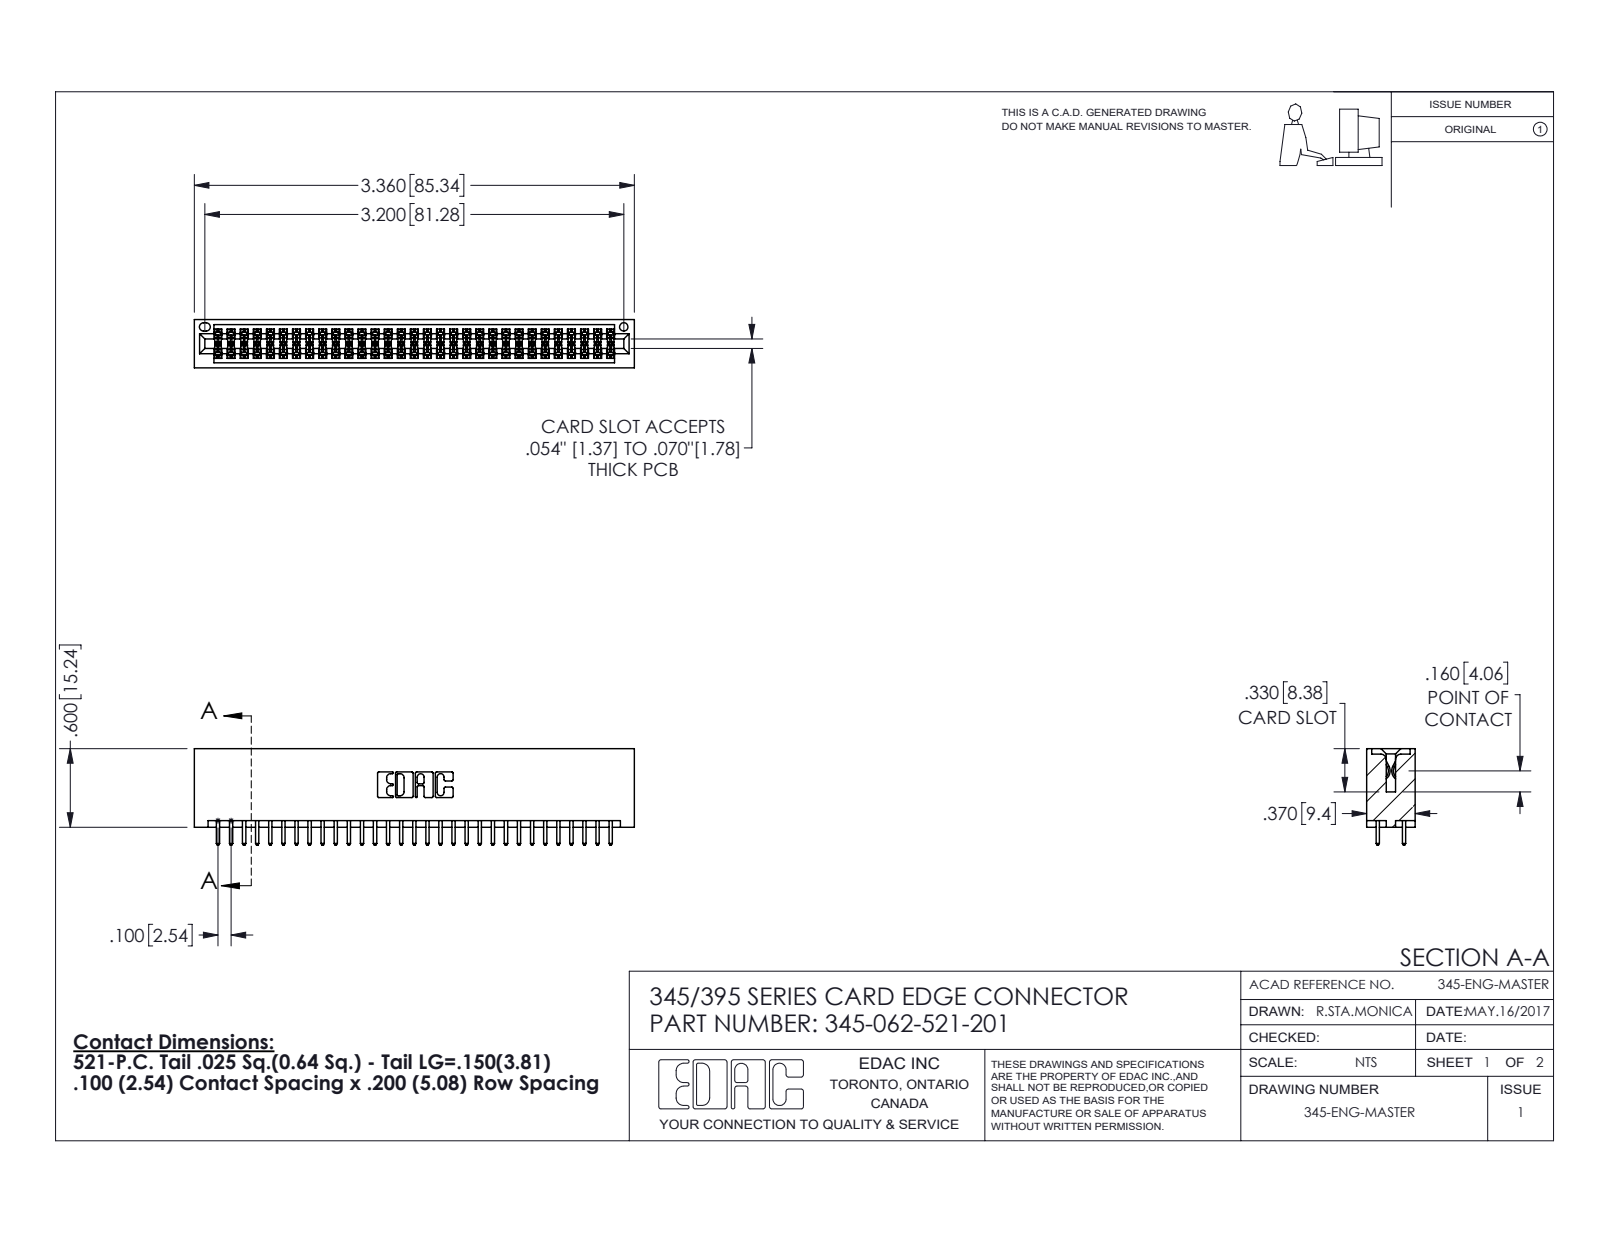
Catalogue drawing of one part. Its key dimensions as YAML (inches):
part_name: "345 Part_No Mounting Lugs; 345-292-001_345-293-121; 345-062-521-201"
step_written_by: "SolidWorks 2016 (CONFIG_CONTROL_DESIGN)"
units: inches
bodies: {solids: 63, faces: 3218, planar: 2122, cylindrical: 1096, other: 0}
overall_size: [3.36, 0.737, 0.37]
volume: 0.536
surface_area: 20
round_holes:
  - {diameter: 0.064, count: 1}
partial_cylinders:
  - {radius: 0.006, count: 93}
  - {radius: 0.01, count: 62}
  - {radius: 0.01, count: 22}
  - {radius: 0.007, count: 6}
  - {radius: 0.031, count: 6}
  - {radius: 0.026, count: 3}
  - {radius: 0.014, count: 2}
  - {radius: 0.019, count: 2}
face_to_face_distances: [0.298, 0.072, 0.2, 0.098, 0.272, 0.025, 0.37, 0.225, 0.175, 0.149]
